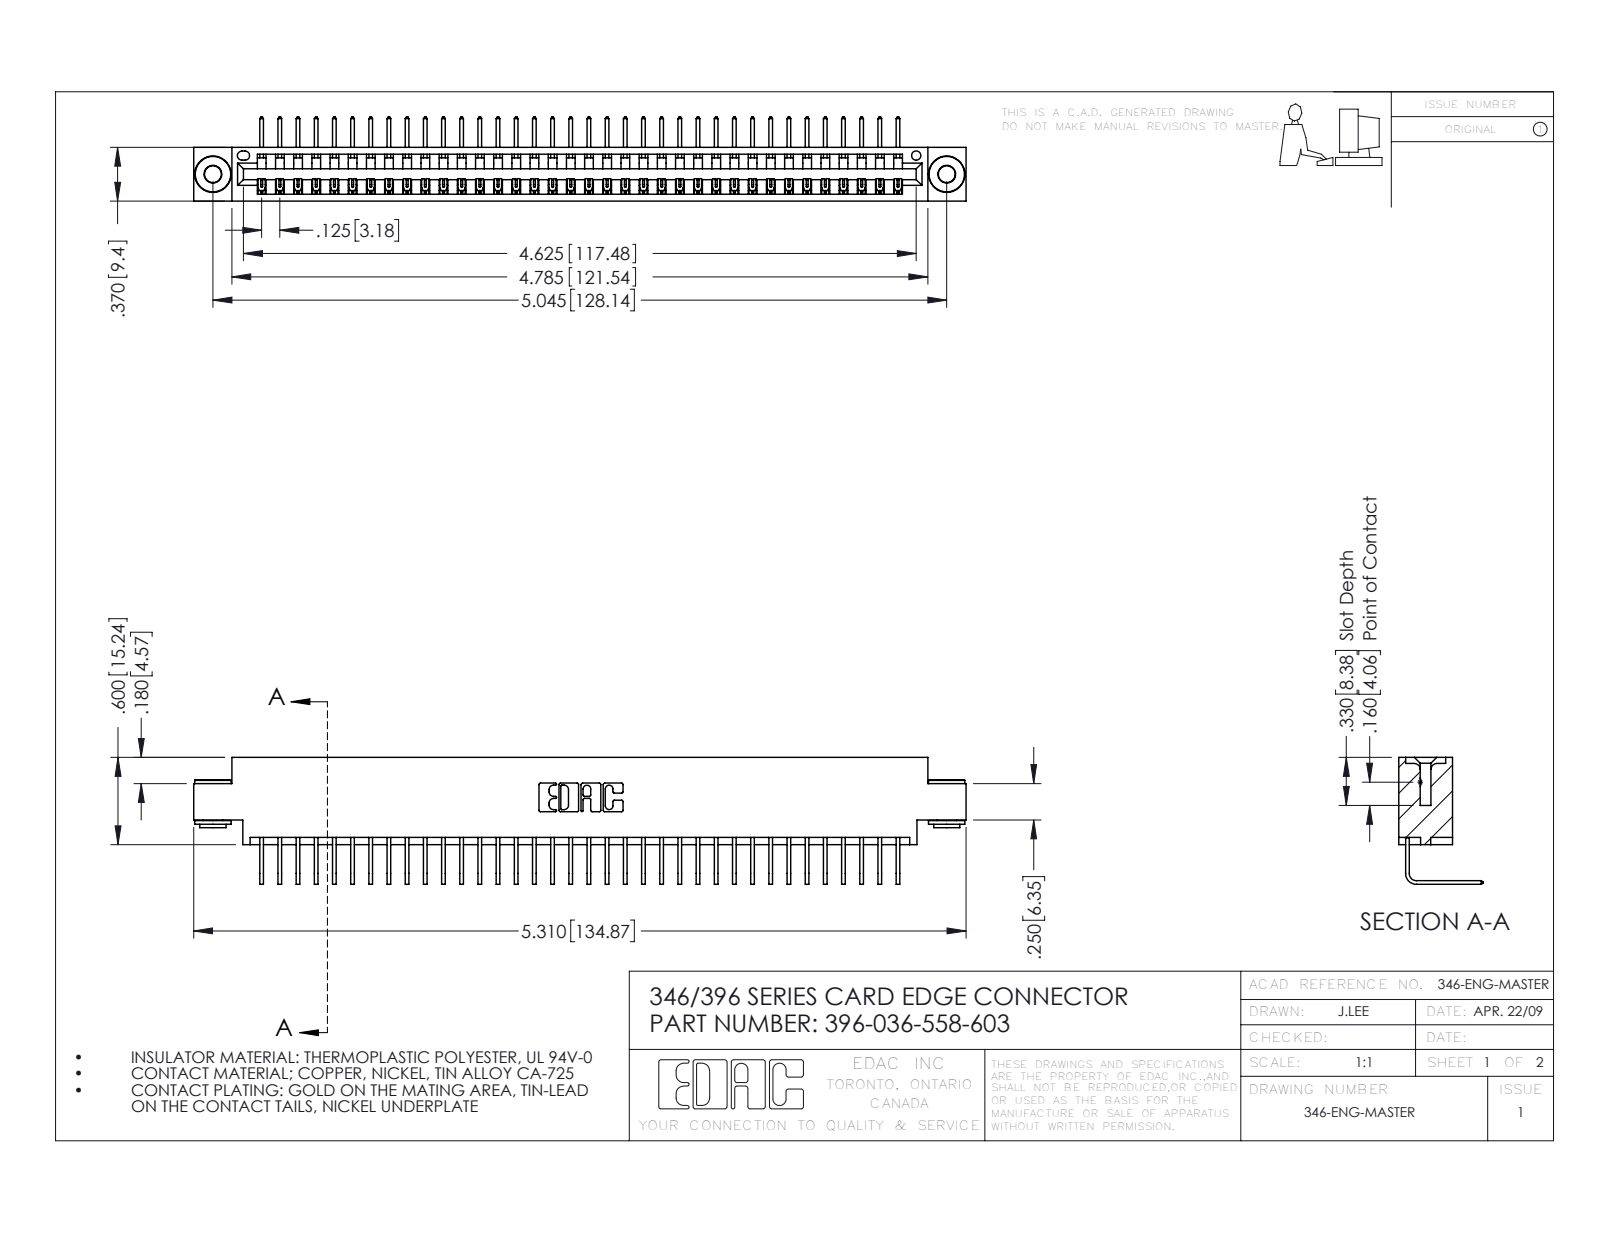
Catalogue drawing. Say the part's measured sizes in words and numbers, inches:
The part is named "345-292-001_558 Tail - 2; 345-250-002_345-250-002-102; 396-036-558-603; 346 Part_0.170 Offset - 0.156 Dia-TH". Its 3-D file was written by "SolidWorks 2016 (CONFIG_CONTROL_DESIGN)". It is 39 solids with 2324 faces: 1602 planar, 714 cylindrical and 8 other. Overall it measures 5.31 by 0.873 by 0.58 inches. Its volume is 0.784 cubic inches and its surface area 26.5 square inches. Round holes: 2 of diameter 0.116, 2 of diameter 0.156, 1 of diameter 0.064. Round bosses or shafts: 2 of diameter 0.25, 2 of diameter 0.18, 2 of diameter 0.136. Partial cylindrical surfaces (rounded edges, fillets, slot ends): 72 of radius 0.006, 22 of radius 0.01, 6 of radius 0.007, 6 of radius 0.031, 3 of radius 0.026, 2 of radius 0.031, 2 of radius 0.04, 1 of radius 0.014. The main face-to-face distances are 0.322, 0.048, 0.37, 0.25, 0.025, 0.298, 0.072, 0.148, 0.222, 0.1. The hole center spacings are 0.246, 4.836, 5.045.
